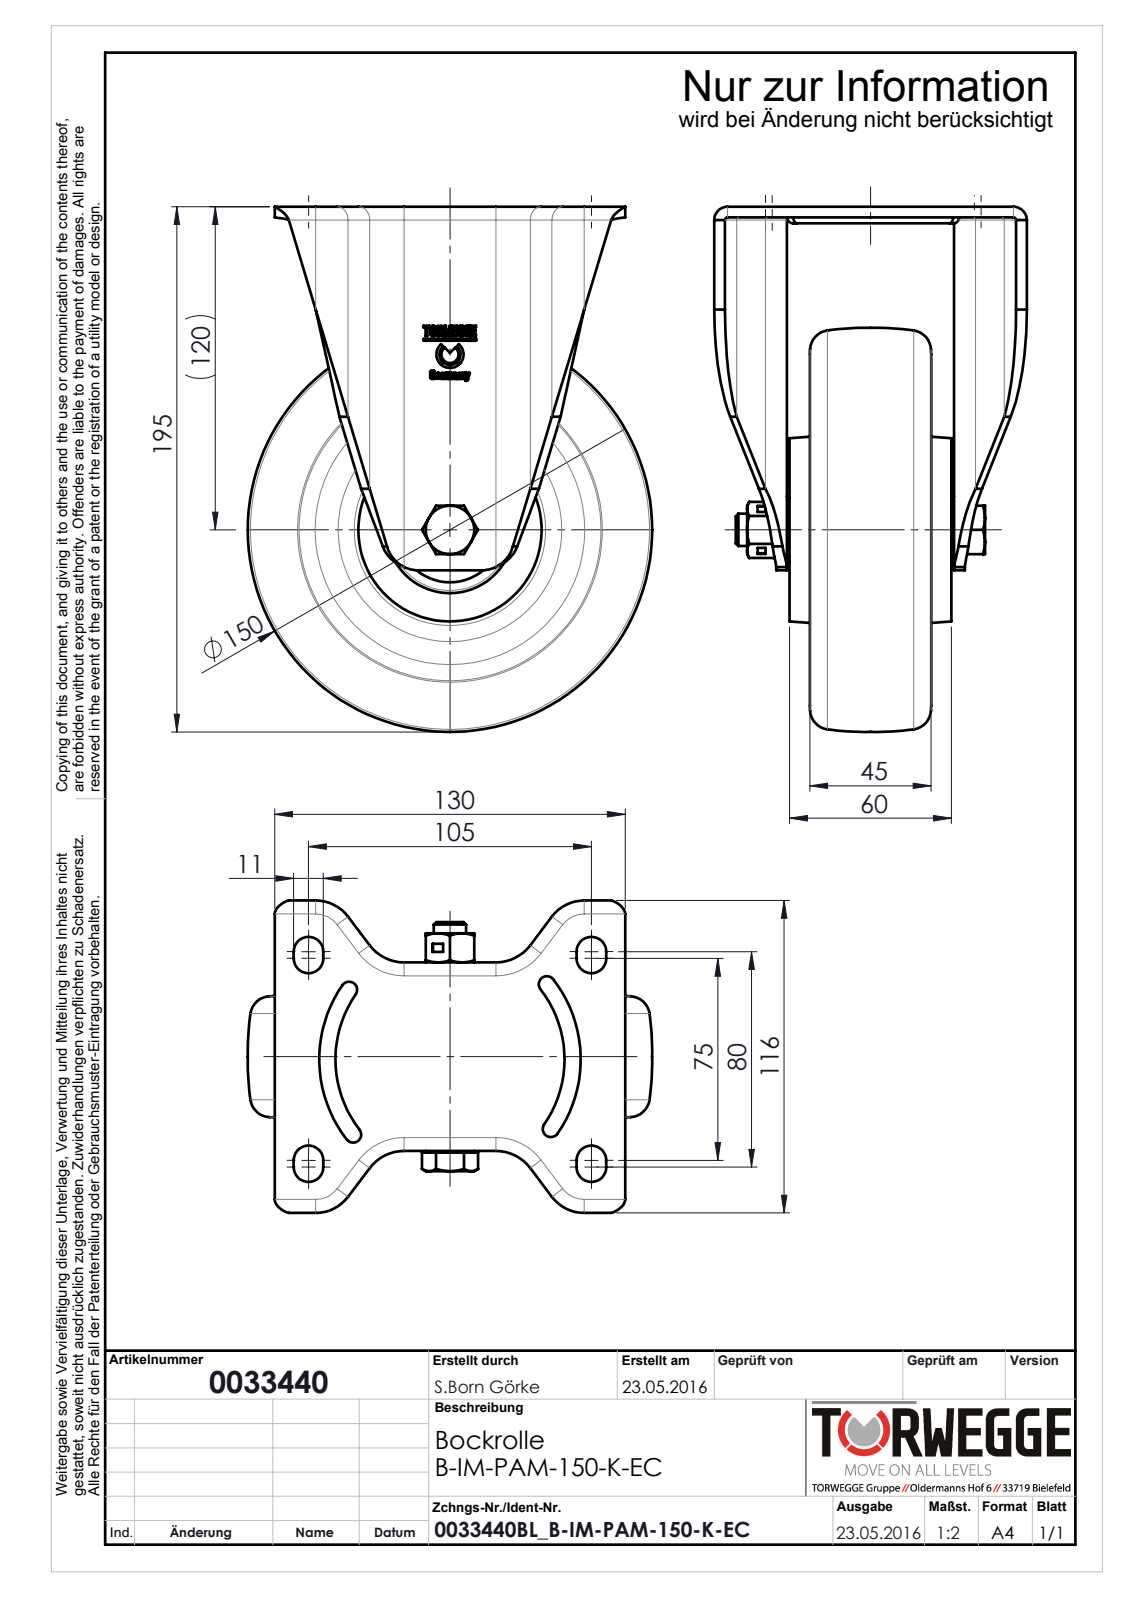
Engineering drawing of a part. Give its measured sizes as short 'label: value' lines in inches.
name: 0033440BL_B-IM-PAM-150-K-EC
written by: SolidWorks 2016 (AUTOMOTIVE_DESIGN)
unit: in
bodies: 9 solids, 668 faces (325 planar, 195 cylindrical, 148 other)
size: 7.678 × 5.907 × 4.567
volume: 45.28 in³; area: 288.6 in²
holes: 1× ⌀0.402, 1× ⌀0.472, 1× ⌀0.48, 1× ⌀0.787, 1× ⌀0.807, 1× ⌀1.378, 1× ⌀1.531
bosses: 1× ⌀1.85, 1× ⌀1.106, 1× ⌀0.984, 1× ⌀0.945, 1× ⌀0.783, 1× ⌀0.709
rounds: 8× R0.015, 8× R0.039, 8× R0.197, 8× R0.217, 7× R0.008, 7× R0.024, 4× R0.005, 4× R0.034
face distances: 0.157, 2.598, 0.039, 1.378, 0.197, 2.559, 2.402, 1.811, 1.181, 1.575
